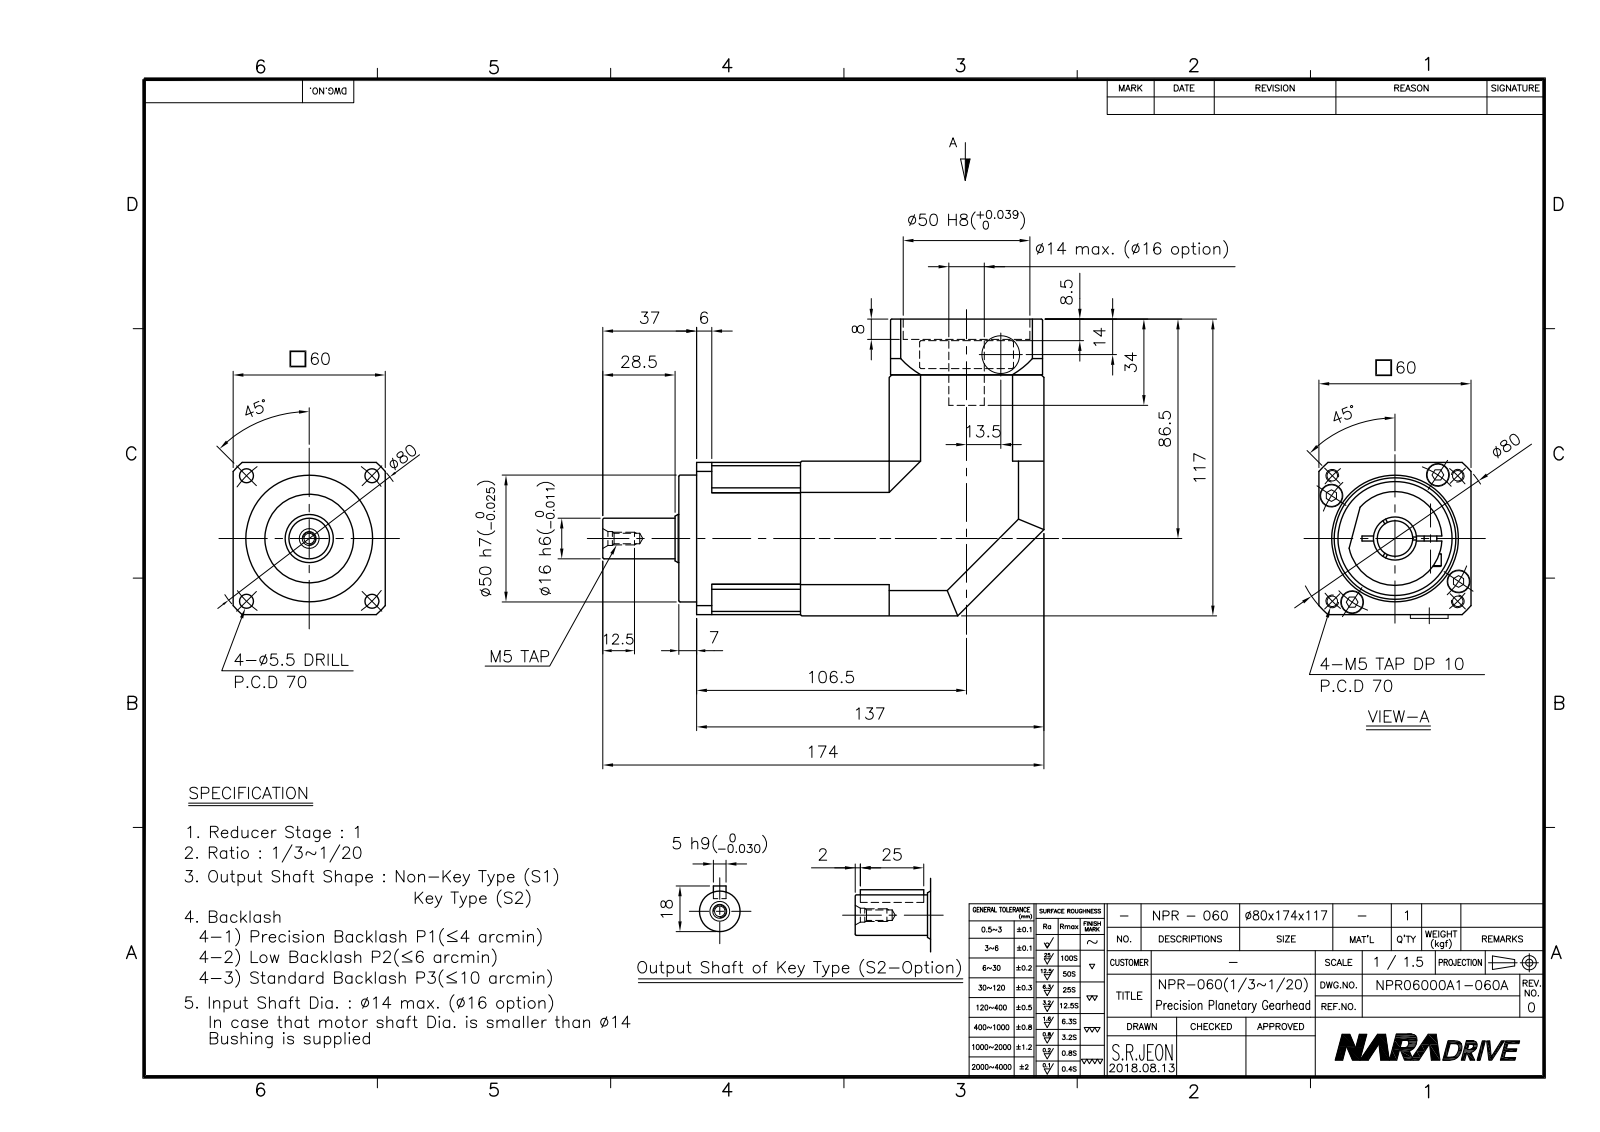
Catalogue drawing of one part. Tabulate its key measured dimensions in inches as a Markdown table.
| quantity | value |
| --- | --- |
| part name | NPR06000A1-060A-S1 |
| STEP written by | Autodesk Inventor 2015 (AUTOMOTIVE_DESIGN) |
| units | inches |
| bodies | 2 solids, 400 faces (196 planar, 108 cylindrical, 96 other) |
| overall size | 6.85 × 4.606 × 2.441 |
| volume | 34.46 in³ |
| surface area | 127.9 in² |
| round holes (diameter × count) | 0.163 × 9, 0.217 × 9, 0.128 × 4, 0.177 × 4, 0.315 × 4, 0.354 × 4, 0.276 × 1, 0.335 × 1, 0.551 × 1, 0.669 × 1, 1.772 × 1, 1.89 × 1 |
| round bosses / shafts (diameter × count) | 0.335 × 5, 0.197 × 5, 0.276 × 4, 0.157 × 4, 1.969 × 1, 1.457 × 1, 1.378 × 1, 0.748 × 1 |
| partial cylindrical surfaces (radius × count) | 0.02 × 4, 0.276 × 4, 1.398 × 2, 1.575 × 2, 0.081 × 1, 0.177 × 1, 1.378 × 1 |
| main face-to-face distances | 0.02, 2.382, 2.402, 2.362, 3.268, 1.457, 3.858, 0.315, 3.543, 3.839 |
| hole center spacings | 1.191, 1.378, 1.684, 1.949, 0.345, 2.552, 1.606, 2.014 |
